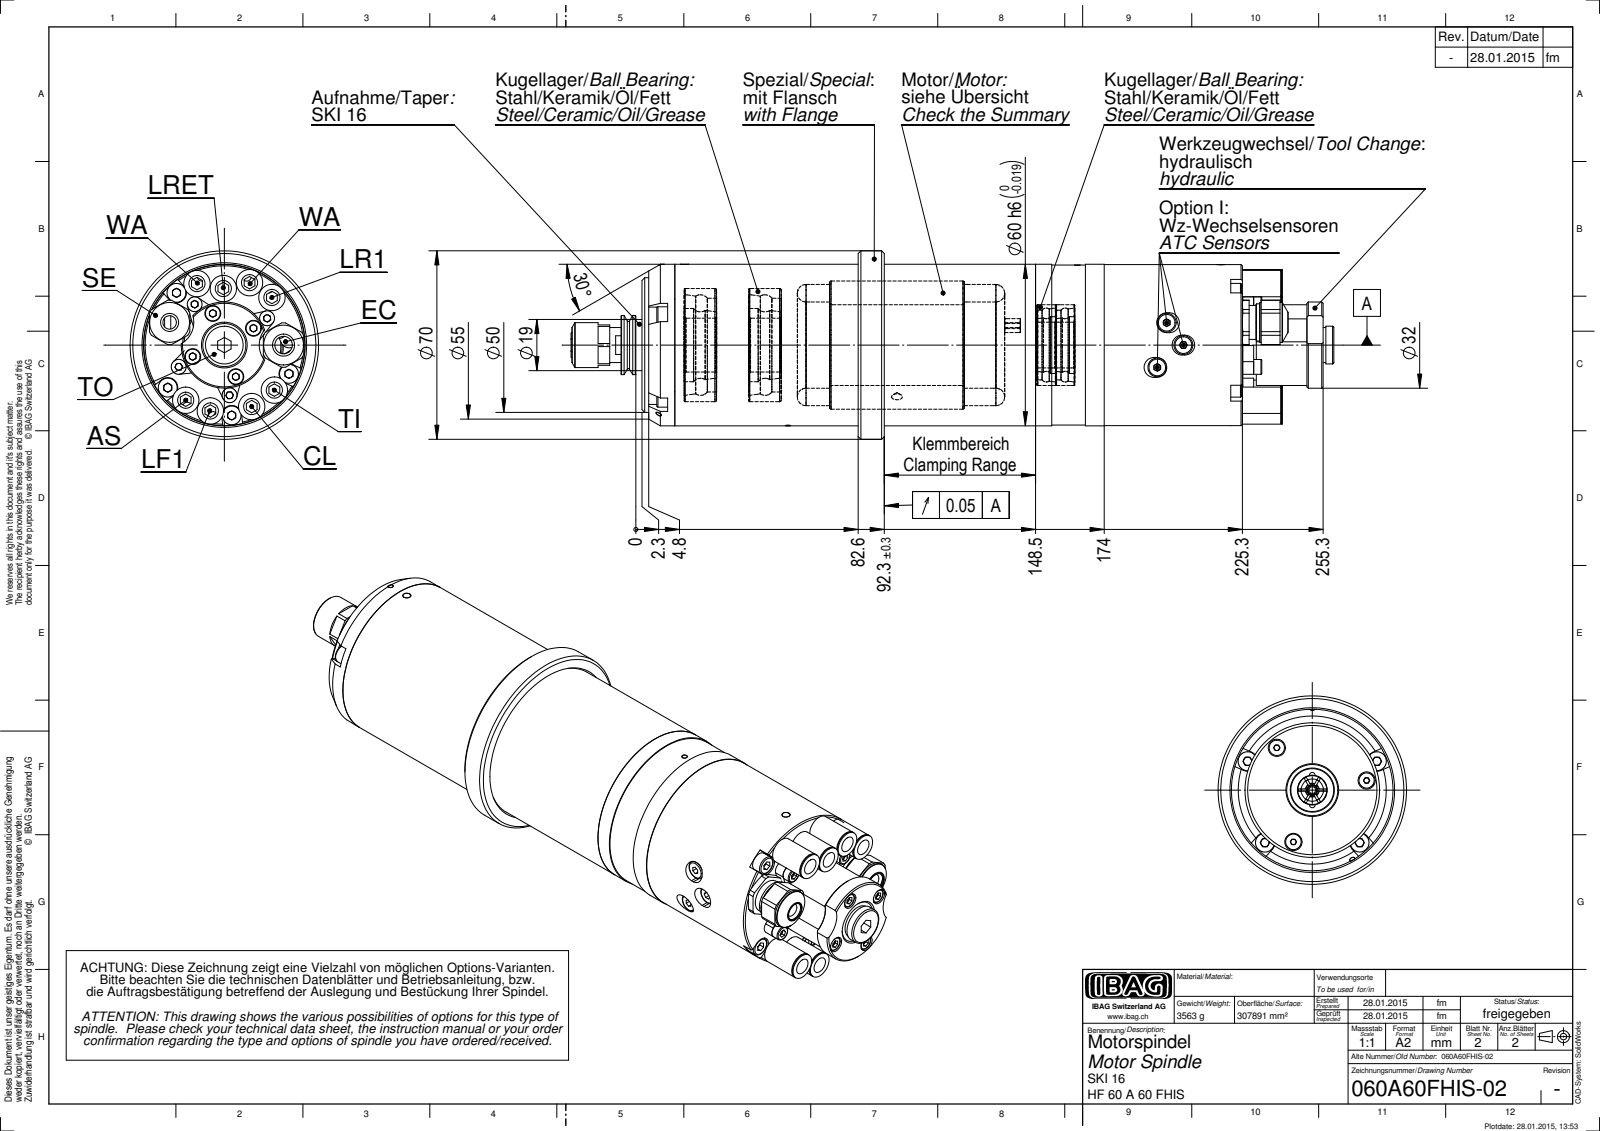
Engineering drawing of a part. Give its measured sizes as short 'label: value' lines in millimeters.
name: 060A60FHIS-02
written by: SolidWorks 2014 (CONFIG_CONTROL_DESIGN)
unit: mm
bodies: 0 solids, 675 faces (310 planar, 210 cylindrical, 155 other)
size: 283.35 × 70 × 70
holes: 8× ⌀6, 4× ⌀5.9, 1× ⌀2, 1× ⌀4.2, 1× ⌀5, 1× ⌀6.5, 1× ⌀6.7, 1× ⌀8.2
bosses: 10× ⌀7, 8× ⌀9.8, 4× ⌀5.5, 3× ⌀5.7, 2× ⌀14.8, 2× ⌀13.79, 2× ⌀12.59, 1× ⌀70
rounds: 14× R3.7, 2× R8.25, 2× R9, 1× R16
face distances: 220.5, 2.5, 223, 9.7, 146.2, 143.7, 76.8, 77.8, 171.7, 169.2
hole spacings: 25, 12.51, 9.97, 12.56, 17.69, 22, 36.72, 37.49
